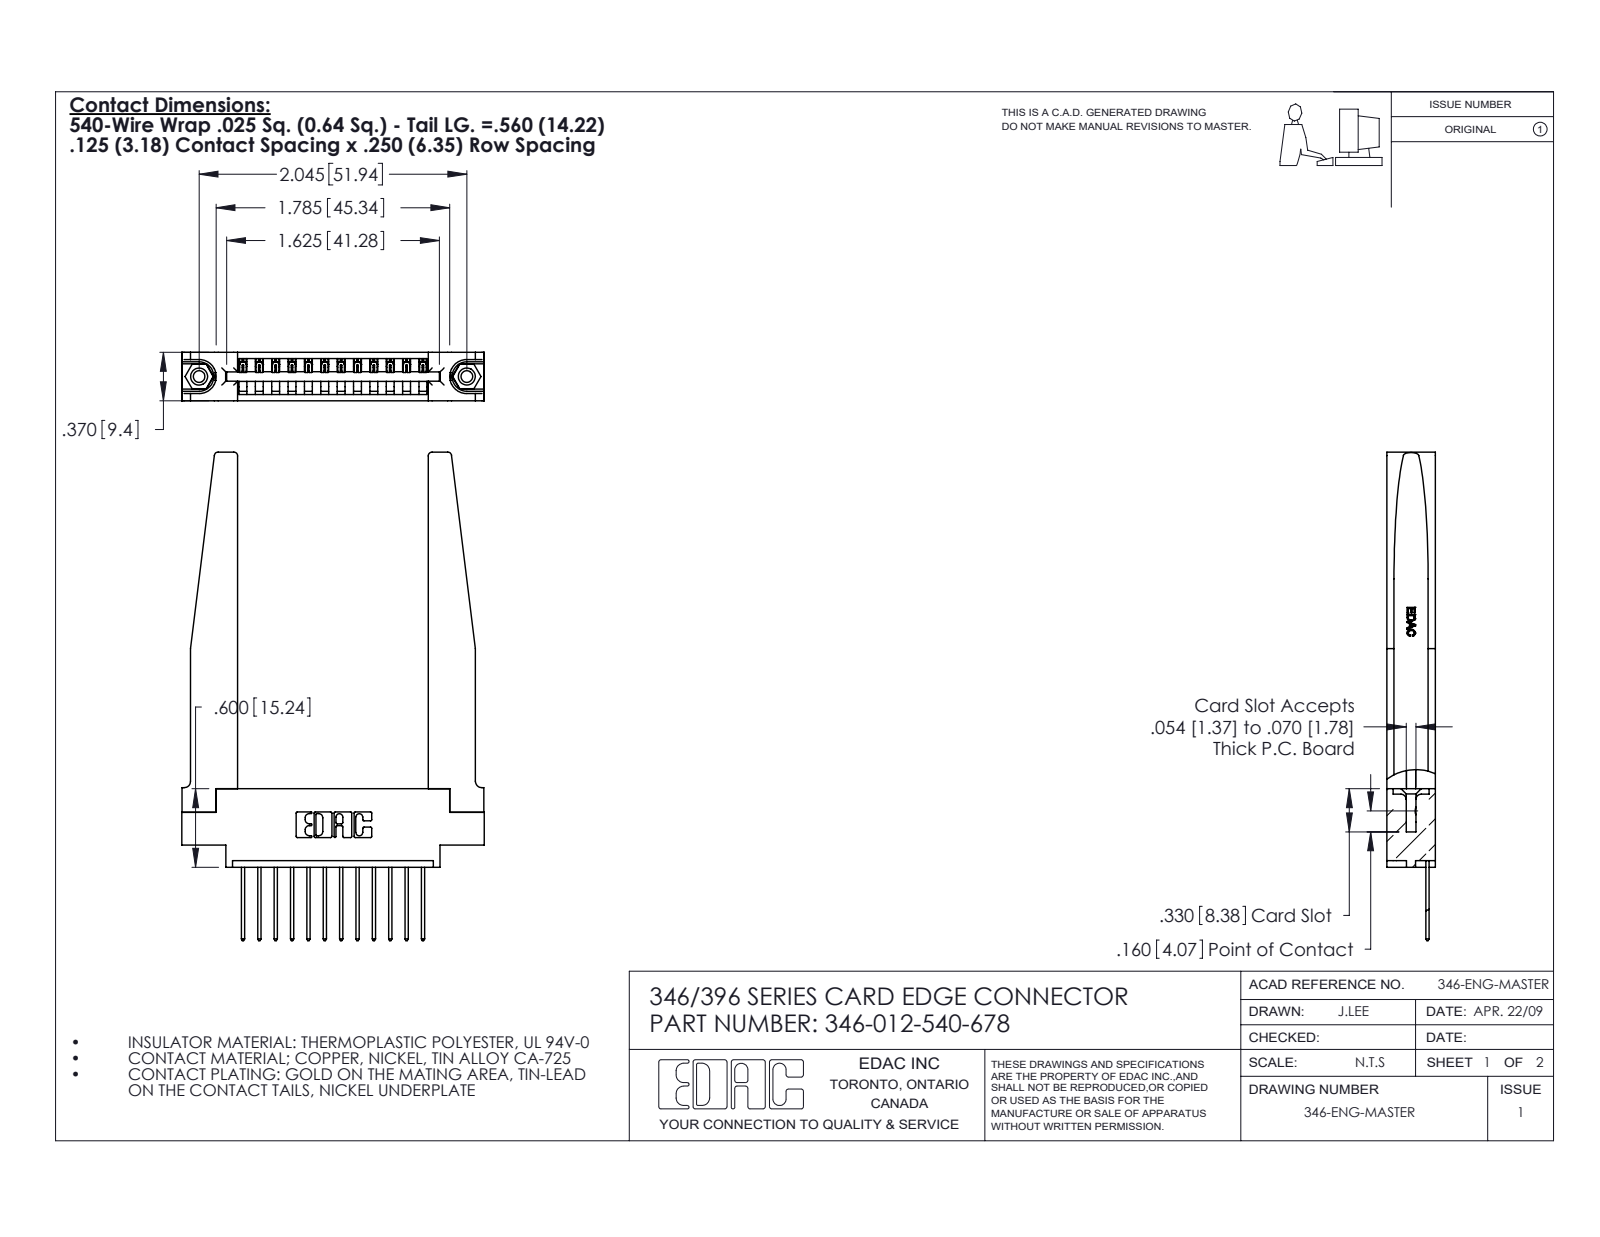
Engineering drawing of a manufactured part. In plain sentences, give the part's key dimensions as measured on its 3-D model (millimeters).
The part is named "345-250-001_345-250-001-102; 346-012-540-678; 346-220-078_345-220-078; 346 Part_0.170 Offset - 0.156 Dia-TH (+1 more)". Its 3-D file was written by "SolidWorks 2020 (CONFIG_CONTROL_DESIGN)". It is 17 solids with 1070 faces: 716 planar, 302 cylindrical and 52 other. Overall it measures 94.7 by 58.7 by 9.4 millimeters. Its volume is 12 200 cubic millimeters and its surface area 13 090 square millimeters. Round holes: 2 of diameter 2.3, 2 of diameter 3.2, 2 of diameter 4, 1 of diameter 1.6. Round bosses or shafts: 2 of diameter 3.9. Partial cylindrical surfaces (rounded edges, fillets, slot ends): 24 of radius 0.2, 24 of radius 0.3, 22 of radius 0.3, 8 of radius 0.8, 6 of radius 0.2, 6 of radius 0.8, 3 of radius 0.7, 2 of radius 0.8. The main face-to-face distances are 9.4, 3.8, 1.8, 3.8, 1.2, 8.2, 6.4, 5.6, 2.6, 4.4. The hole center spacings are 6.2, 46.7, 51.9.
